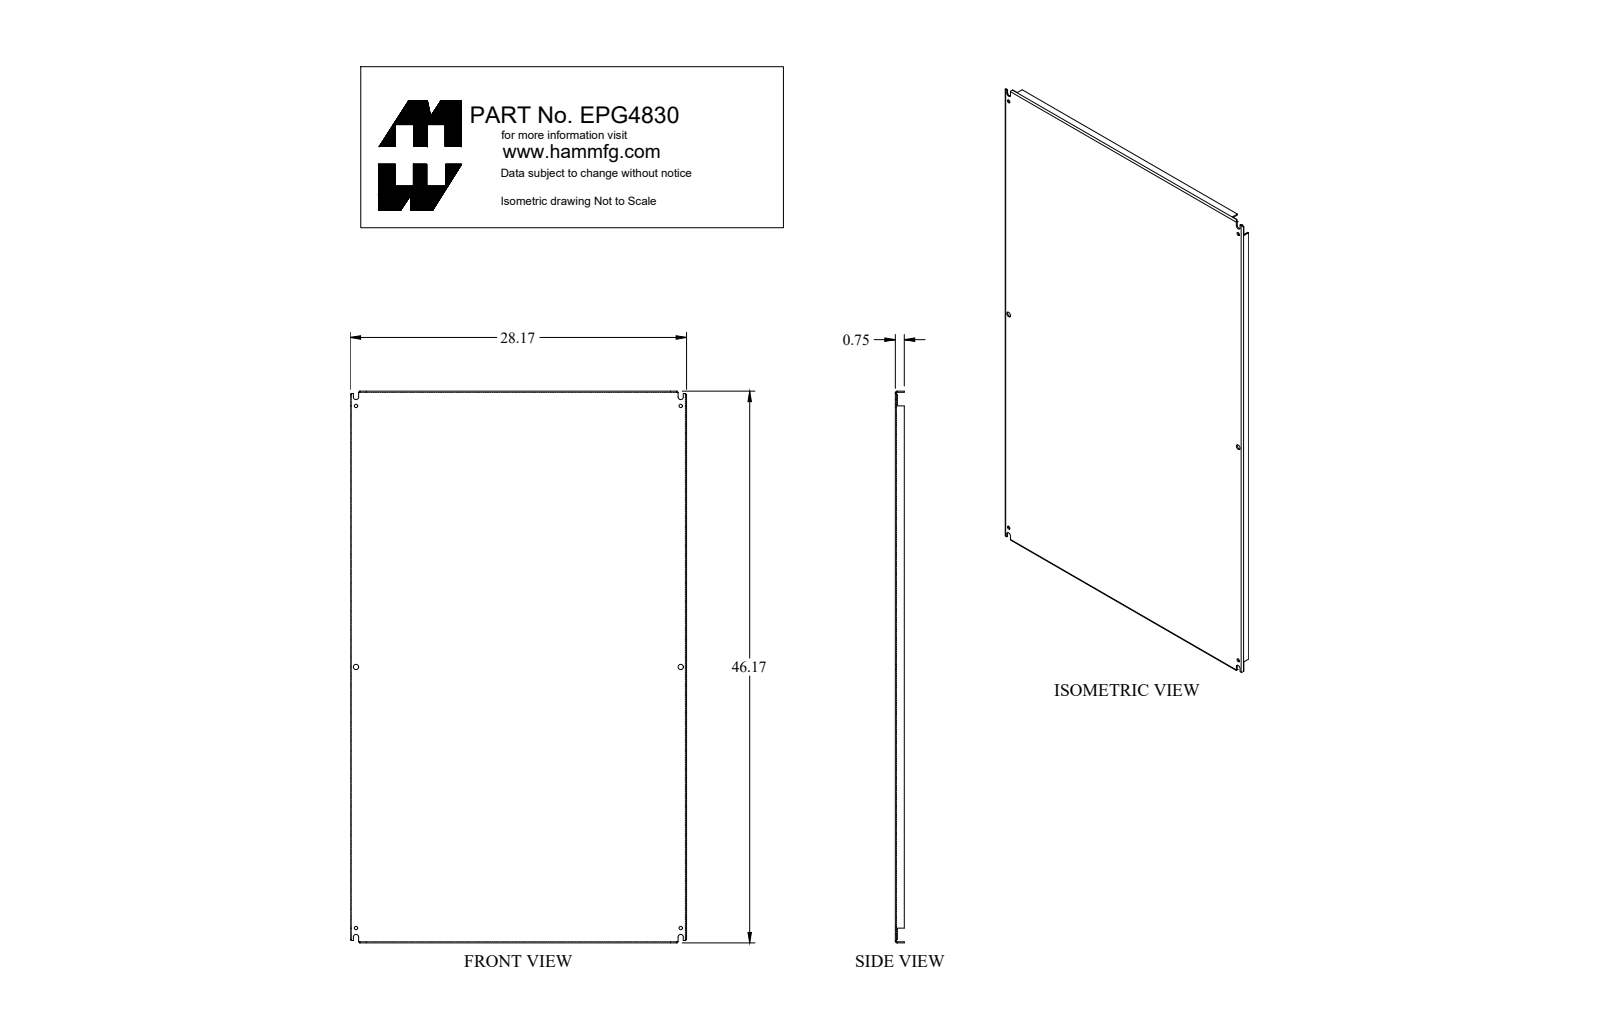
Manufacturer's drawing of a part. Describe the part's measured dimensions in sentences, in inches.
The part is named "EPG4830". Its 3-D file was written by "SolidWorks 2018 (AUTOMOTIVE_DESIGN)". It is 1 solid with 132 faces: 74 planar, 42 cylindrical and 16 other. Overall it measures 46.17 by 28.17 by 0.75 inches. Its volume is 131.4 cubic inches and its surface area 2 783 square inches. Round holes: 4 of diameter 0.281, 2 of diameter 0.437. Partial cylindrical surfaces (rounded edges, fillets, slot ends): 4 of radius 0.048, 4 of radius 0.063, 4 of radius 0.143, 4 of radius 0.219. The main face-to-face distances are 0.095, 28.075, 46.075, 27.98, 28.17, 45.98, 46.17, 0.75, 0.655, 0.171. The hole center spacings are 21.844, 34.876, 27.188, 43.688, 51.457.
